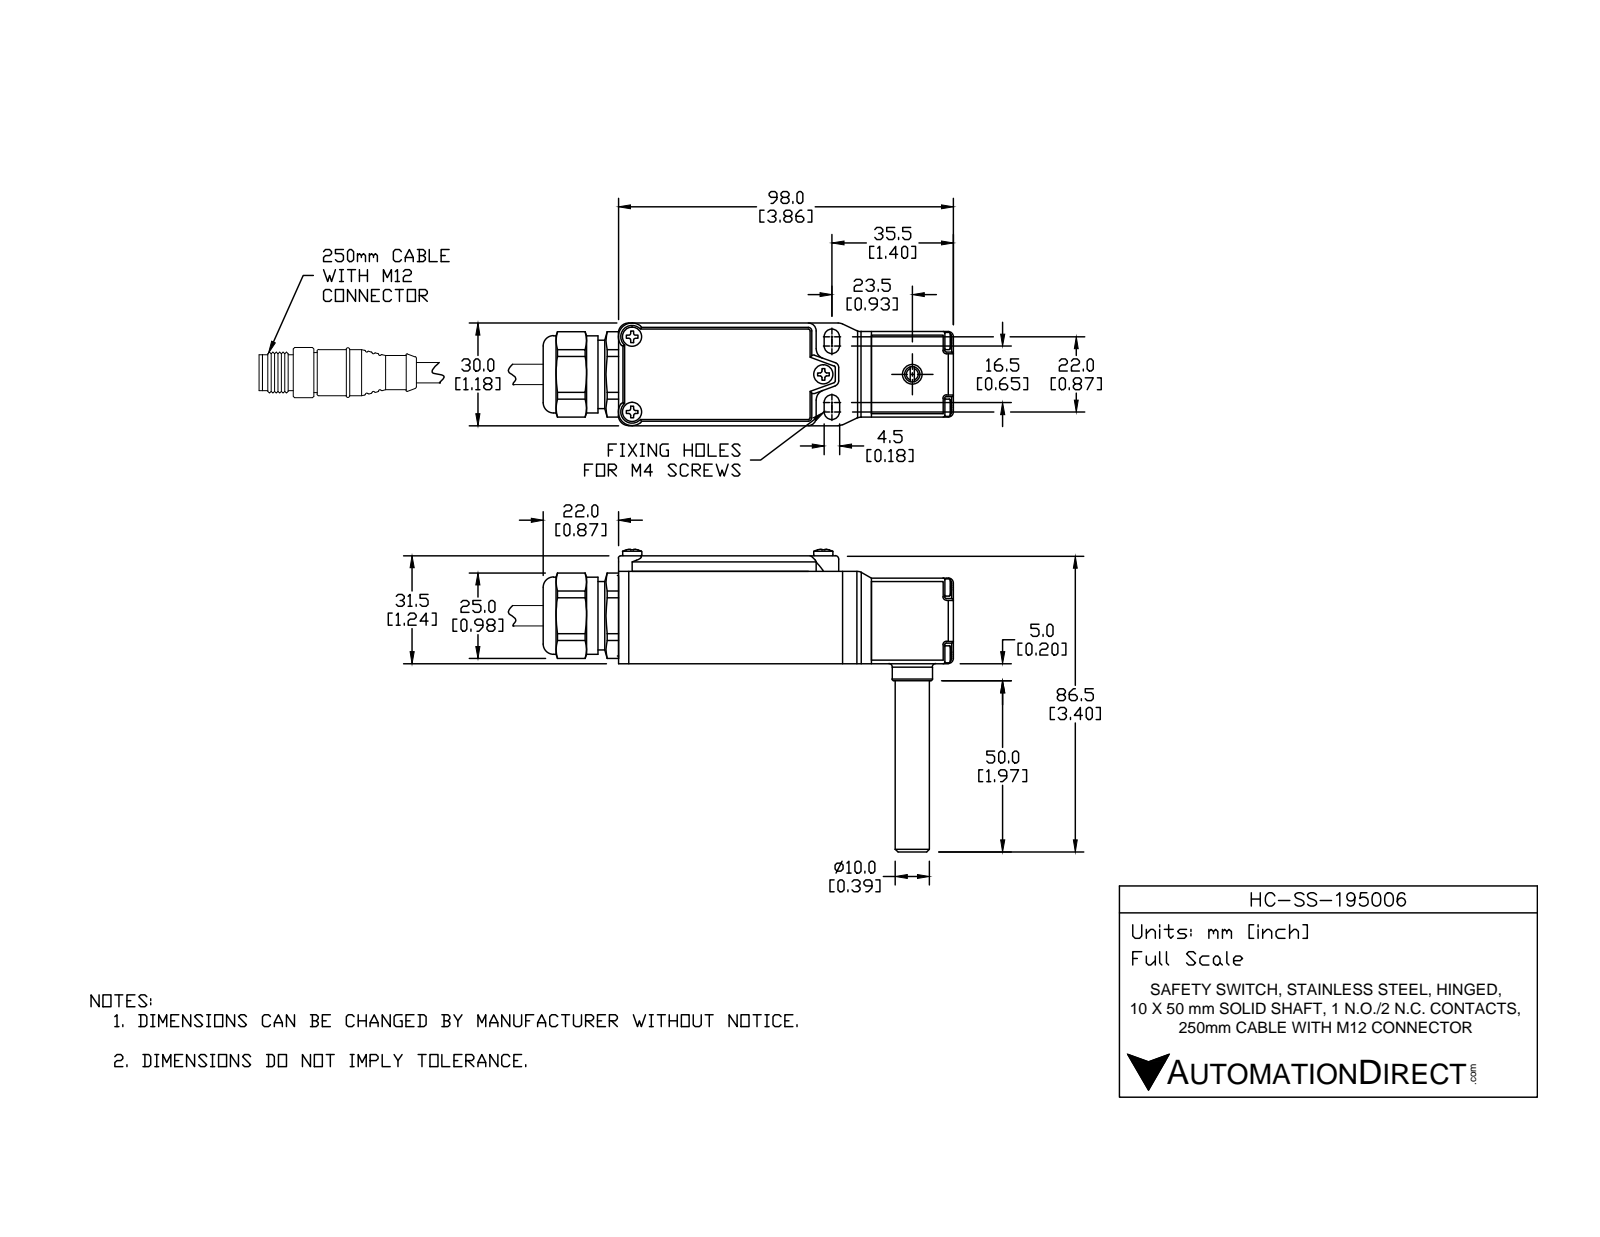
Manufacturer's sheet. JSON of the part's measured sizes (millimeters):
{"part_name": "HC-SS-195006", "step_written_by": "SolidWorks 2014 (AUTOMOTIVE_DESIGN)", "units": "millimeters", "bodies": {"solids": 13, "faces": 1168, "planar": 347, "cylindrical": 466, "other": 355}, "overall_size": [99, 88.4, 30], "volume_mm3": 43410, "surface_area_mm2": 34190, "round_holes": [[2.5, 8], [3.2, 7], [4, 3], [1.5, 2], [1.8, 2], [2.2, 2], [3.6, 2], [2.1, 1], [2.9, 1], [4.4, 1], [4.7, 1], [5.5, 1]], "round_bosses_or_shafts": [[3, 7], [5, 5], [3.5, 4], [5.6, 3], [23.5, 1], [17.7, 1], [10, 1], [9.8, 1]], "partial_cylinders_radius": [[0.5, 175], [1, 20], [0.3, 18], [0.2, 14], [0.7, 8], [3, 8], [1.5, 6], [2.3, 4]], "face_to_face_distances": [2.5, 29, 2, 2.9, 27.1, 30, 4.5, 31.5, 0.4, 27.5], "hole_center_spacings": [13.8, 19.5, 4.7, 6.2, 10.5, 10.7, 10.8, 12.1]}
